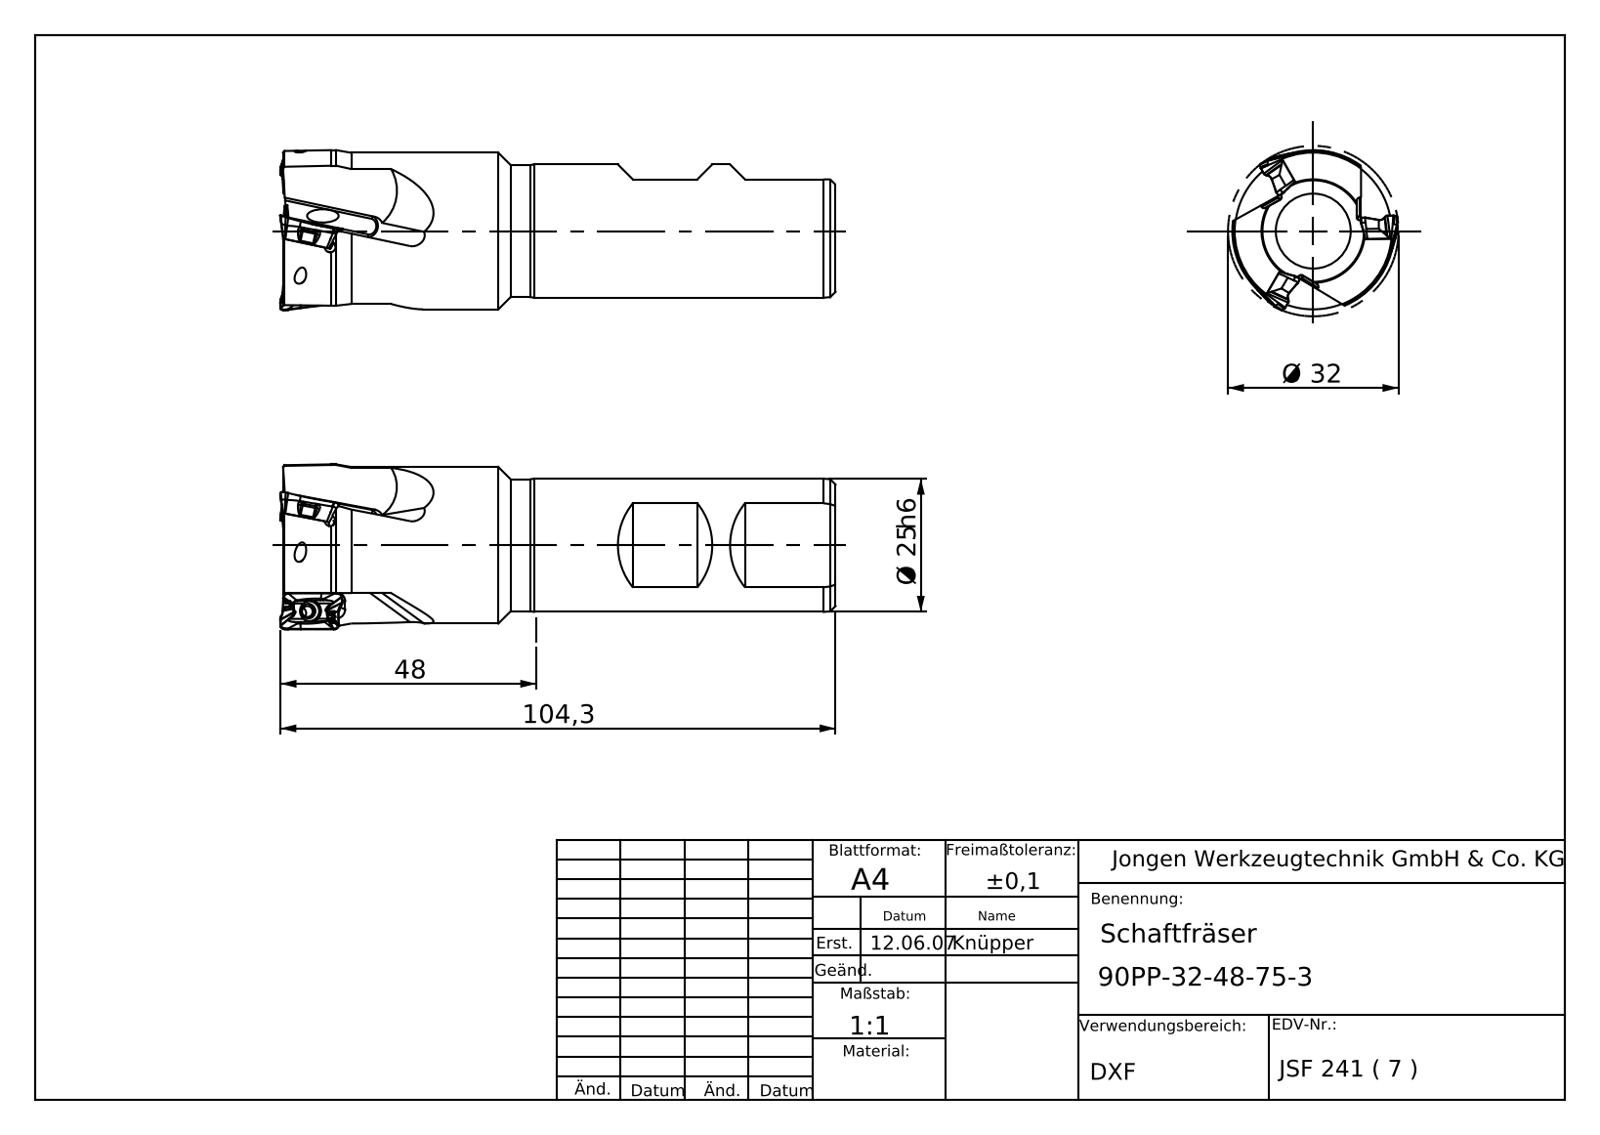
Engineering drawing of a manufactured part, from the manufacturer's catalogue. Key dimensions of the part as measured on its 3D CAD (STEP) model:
Part name (STEP PRODUCT): 90PP-32-48-75-3
STEP written by: SolidWorks 2012 (AUTOMOTIVE_DESIGN)
Units: millimetres
Bodies: 1 solid, 124 faces (50 planar, 34 cylindrical, 40 other)
Overall size (bounding box): 104.3 × 32.17 × 32.16
Volume: 53 427 mm³ · Surface area: 13 186 mm²
Round holes (diameter × count): ⌀2.5 ×3, ⌀6.5 ×1
Round bosses / shafts (diameter × count): ⌀29.38 ×1, ⌀25 ×1, ⌀24.8 ×1
Partial cylindrical surfaces — rounded edges, fillets, slot ends (radius × count): R0.5 ×6, R1.7 ×6, R1.02 ×3
Main face-to-face distances: 102.32, 0.8, 14.88, 11.31, 26.19, 0.5, 1.3, 3.59, 4, 7.59
